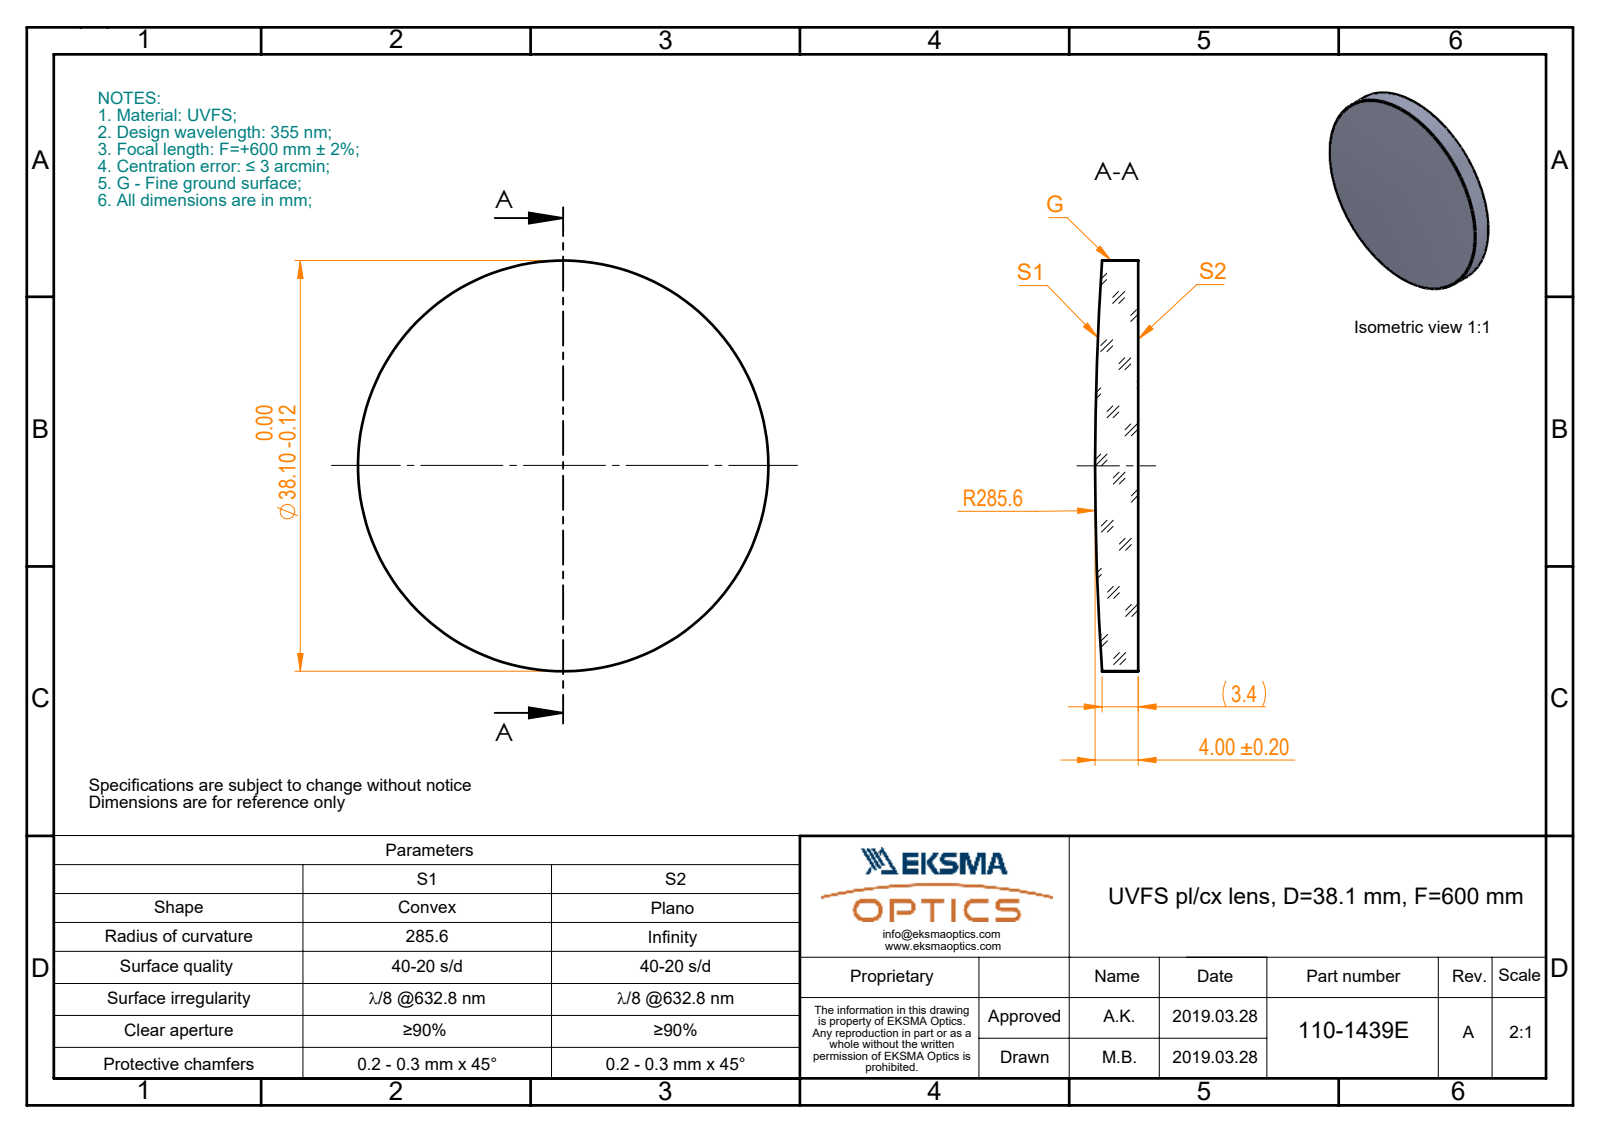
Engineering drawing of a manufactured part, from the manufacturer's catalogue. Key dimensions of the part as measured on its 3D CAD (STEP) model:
Part name (STEP PRODUCT): 110-1439E UVFS pl-cx 38.1 F600
STEP written by: SolidWorks 2017 (CONFIG_CONTROL_DESIGN)
Units: millimetres
Bodies: 1 solid, 5 faces (1 planar, 2 cylindrical, 2 other)
Overall size (bounding box): 38.1 × 38.1 × 4
Volume: 4 198 mm³ · Surface area: 2 684 mm²
Round bosses / shafts (diameter × count): ⌀38.1 ×1
